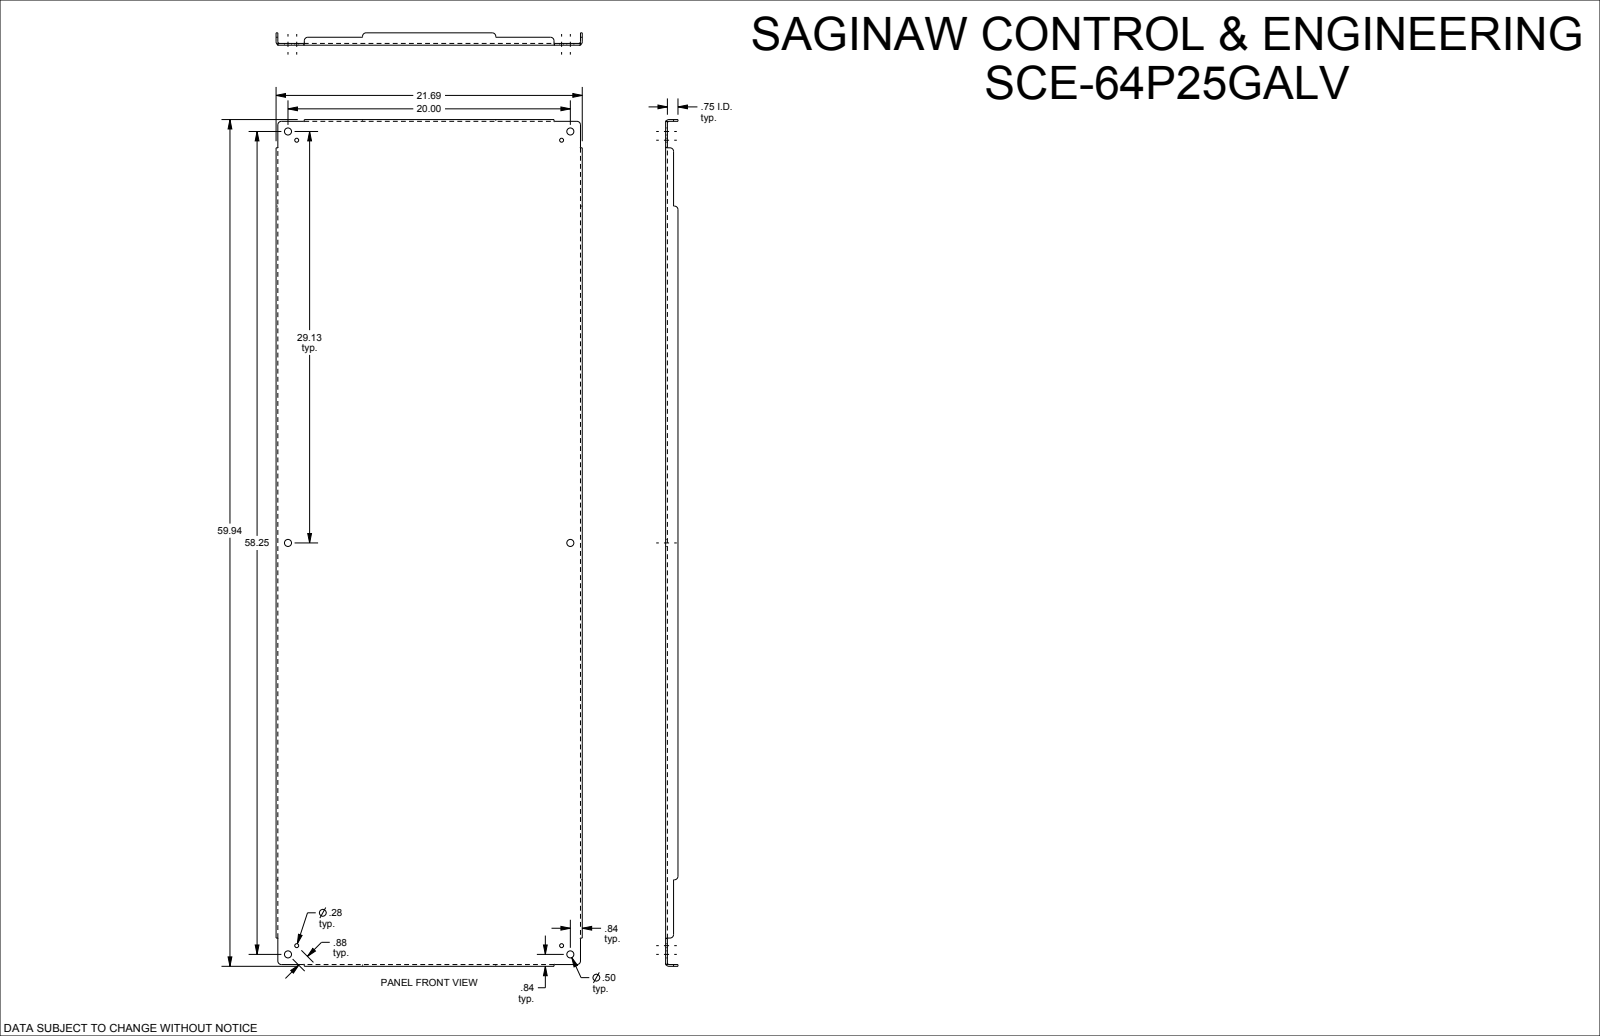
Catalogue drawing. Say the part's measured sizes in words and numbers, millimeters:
The part is named "SCE-64P25GALV". Its 3-D file was written by "SolidWorks 2019 (CONFIG_CONTROL_DESIGN)". It is 1 solid with 108 faces: 46 planar, 38 cylindrical and 24 other. Overall it measures 1522.4 by 550.9 by 22.2 millimeters. Its volume is 2 838 000 cubic millimeters and its surface area 1 802 000 square millimeters. Round holes: 6 of diameter 12.7, 4 of diameter 7.1. Partial cylindrical surfaces (rounded edges, fillets, slot ends): 12 of radius 6.4, 4 of radius 2.8, 4 of radius 6. The main face-to-face distances are 3.2, 547.7, 544.5, 550.8, 3.2, 1519.3, 19.1, 22.2, 1516, 1522.4. The hole center spacings are 22.2, 492.5, 724.2, 739.8, 875.6, 897.4, 1463.9, 1544.4.
